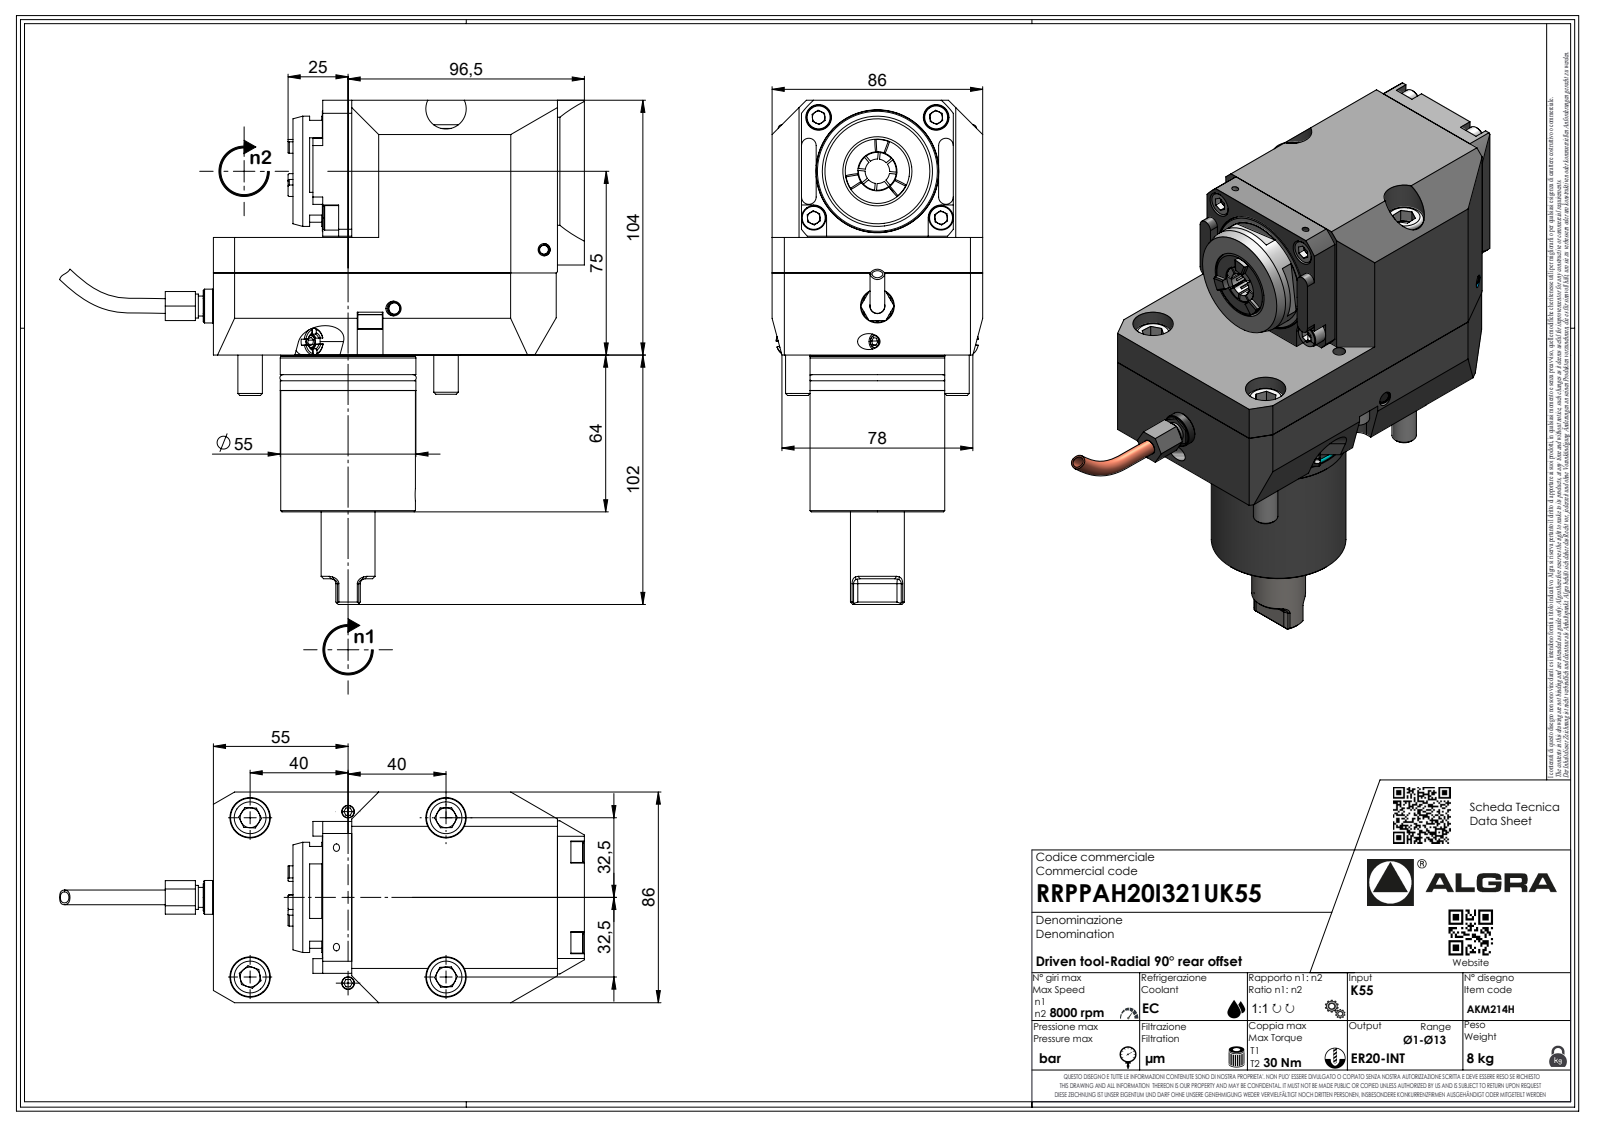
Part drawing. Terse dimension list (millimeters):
name: RRPPAH20I321UK55
written by: SolidWorks 2023 (AUTOMOTIVE_DESIGN)
unit: mm
bodies: 1 solid, 518 faces (340 planar, 68 cylindrical, 110 other)
size: 205.8 × 204.31 × 86
volume: 1 193 000 mm³; area: 86 724 mm²
holes: 2× ⌀16.5, 1× ⌀2.1
bosses: 4× ⌀10, 2× ⌀16, 1× ⌀55.39, 1× ⌀55, 1× ⌀54.99, 1× ⌀52.81, 1× ⌀45, 1× ⌀22
rounds: 7× R0.33, 7× R0.52, 7× R3.7, 6× R2, 4× R3, 2× R5.25, 2× R6.5, 1× R0.21
face distances: 86, 56, 48, 104, 151.5, 47.8, 103.8, 112, 64, 64.2
hole spacings: 65
